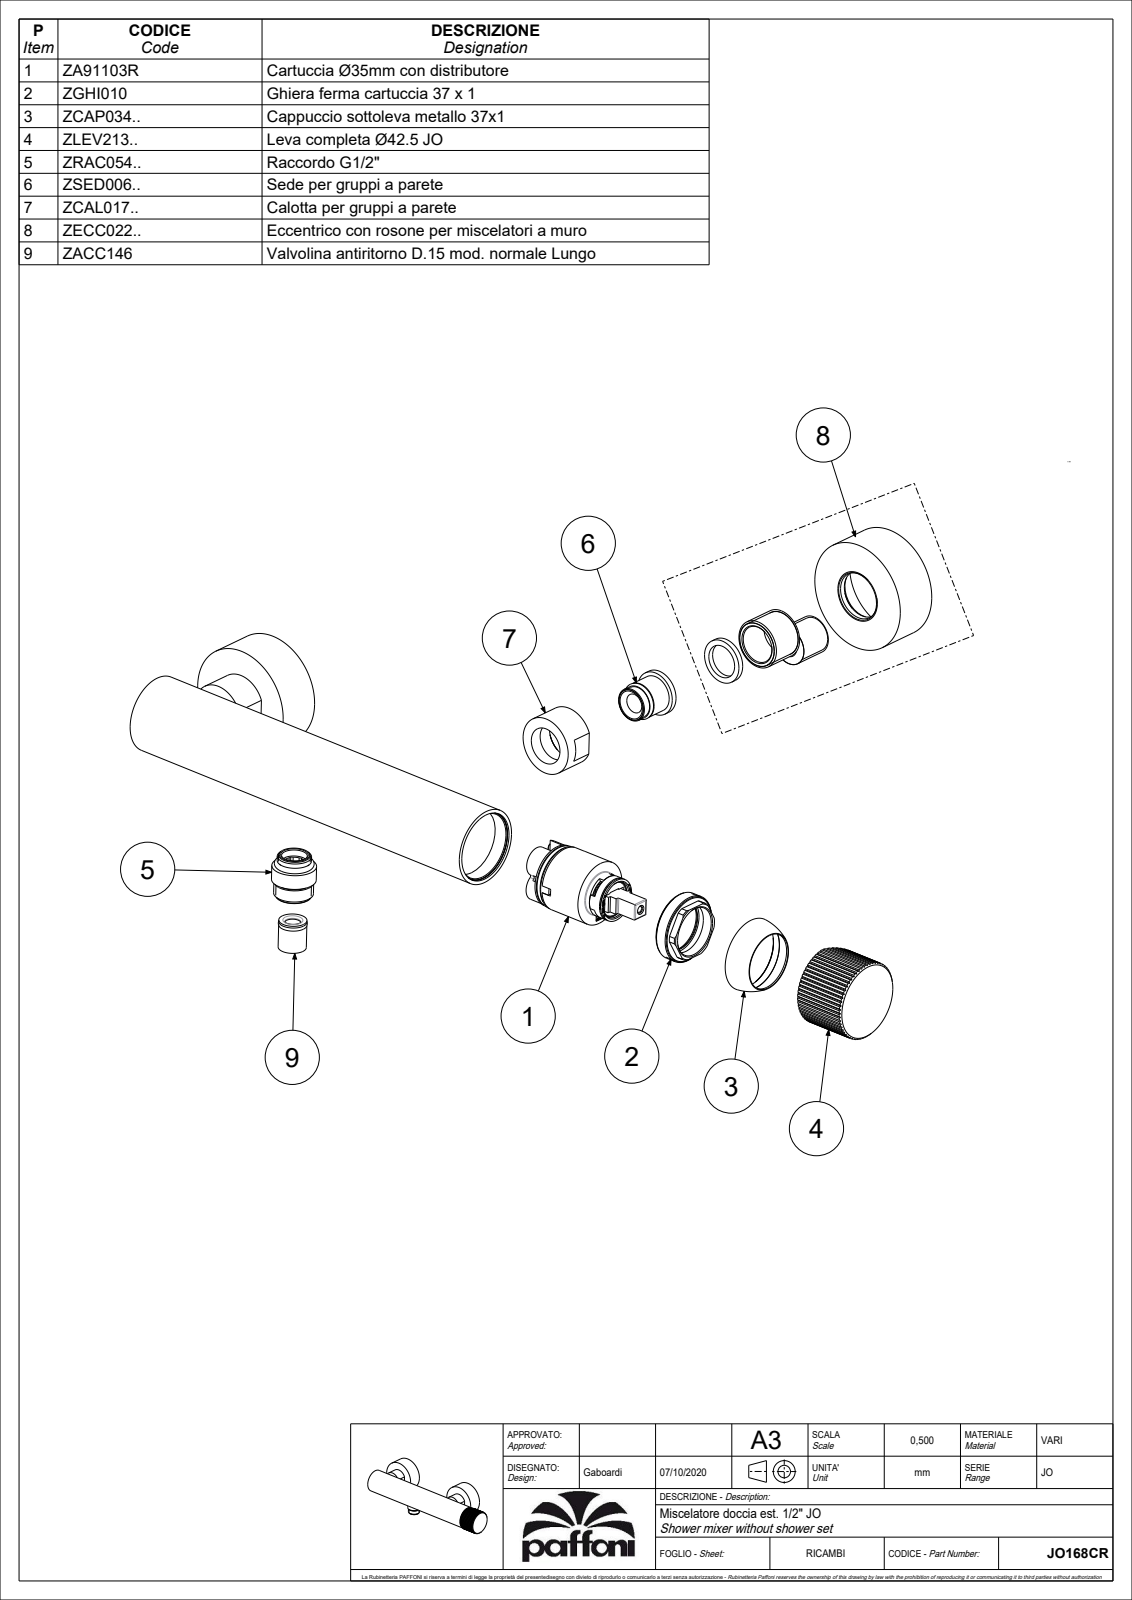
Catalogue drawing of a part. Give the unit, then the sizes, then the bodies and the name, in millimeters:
Units: millimetres
Overall size (bounding box): 269.02 × 86.94 × 63.1
Round holes (diameter × count): ⌀20 ×2, ⌀3 ×1, ⌀5.5 ×1, ⌀8 ×1, ⌀33.5 ×1
Round bosses / shafts (diameter × count): ⌀59.7 ×2, ⌀31.5 ×2, ⌀19.7 ×2, ⌀41.5 ×1, ⌀23.5 ×1, ⌀20.9 ×1, ⌀16.5 ×1, ⌀7.6 ×1
Partial cylindrical surfaces — rounded edges, fillets, slot ends (radius × count): R2.5 ×1, R21.25 ×1
Main face-to-face distances: 25, 18, 43, 16.8, 29.35, 29.34, 29.36, 29, 150, 179
Hole centre spacings: 77.8, 150, 227.8
Volume: 516 325 mm³ · Surface area: 68 428 mm²
Bodies: 1 solid, 286 faces (164 planar, 102 cylindrical, 20 other)
Part name (STEP PRODUCT): JO168CR
STEP written by: CREO PARAMETRIC BY PTC INC, 2020044 (CONFIG_CONTROL_DESIGN)
